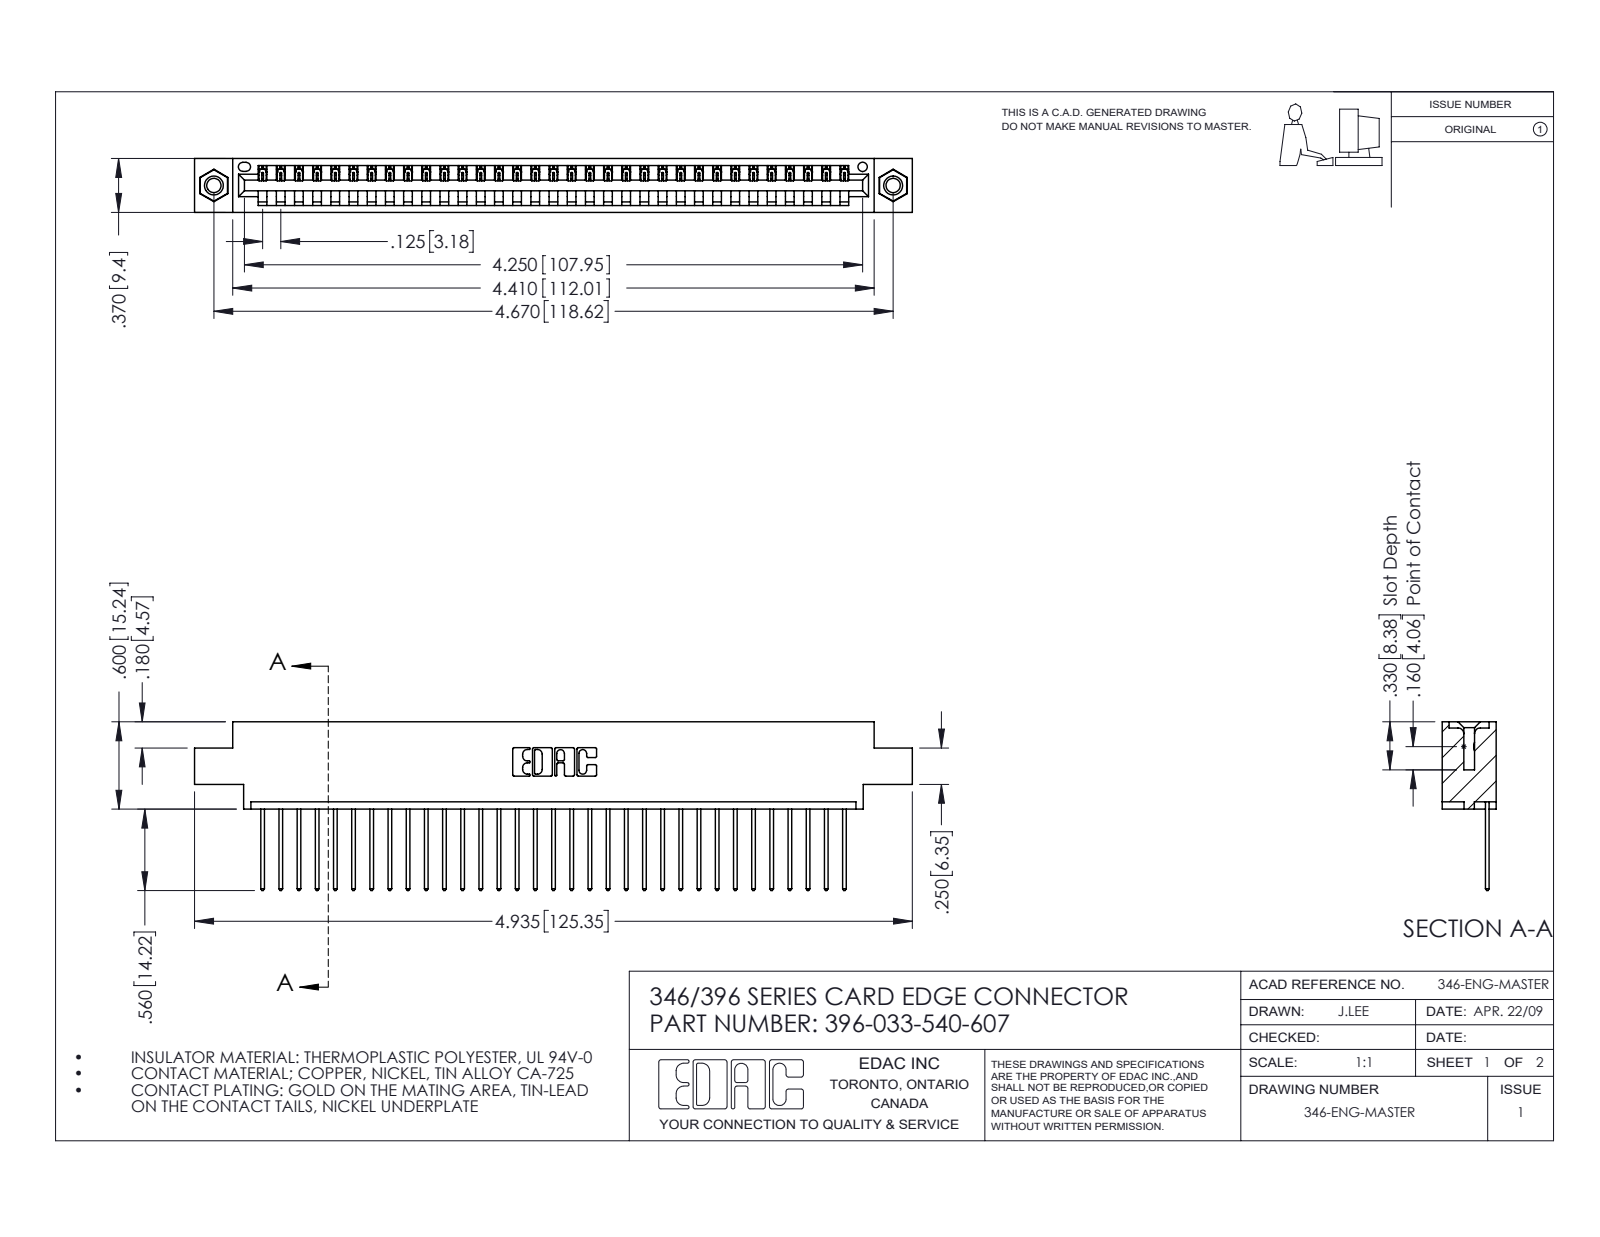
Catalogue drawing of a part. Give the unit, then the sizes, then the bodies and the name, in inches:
Units: inches
Overall size (bounding box): 4.935 × 1.16 × 0.37
Round holes (diameter × count): ⌀0.098 ×2, ⌀0.125 ×2, ⌀0.156 ×2, ⌀0.064 ×1
Round bosses / shafts (diameter × count): ⌀0.155 ×2
Partial cylindrical surfaces — rounded edges, fillets, slot ends (radius × count): R0.006 ×66, R0.01 ×66, R0.01 ×22, R0.007 ×6, R0.031 ×6, R0.026 ×3, R0.031 ×2, R0.04 ×2
Main face-to-face distances: 0.048, 0.322, 0.37, 0.25, 0.072, 0.298, 0.025, 0.222, 0.148, 0.1
Hole centre spacings: 0.246, 4.462, 4.67
Volume: 0.721 in³ · Surface area: 23.54 in²
Bodies: 36 solids, 2100 faces (1432 planar, 652 cylindrical, 16 other)
Part name (STEP PRODUCT): 345-250-001_345-250-005-103; 396-033-540-607; 346 Part_0.170 Offset - 0.156 Dia-TI; 345-292-001_345-293-140
STEP written by: SolidWorks 2016 (CONFIG_CONTROL_DESIGN)
